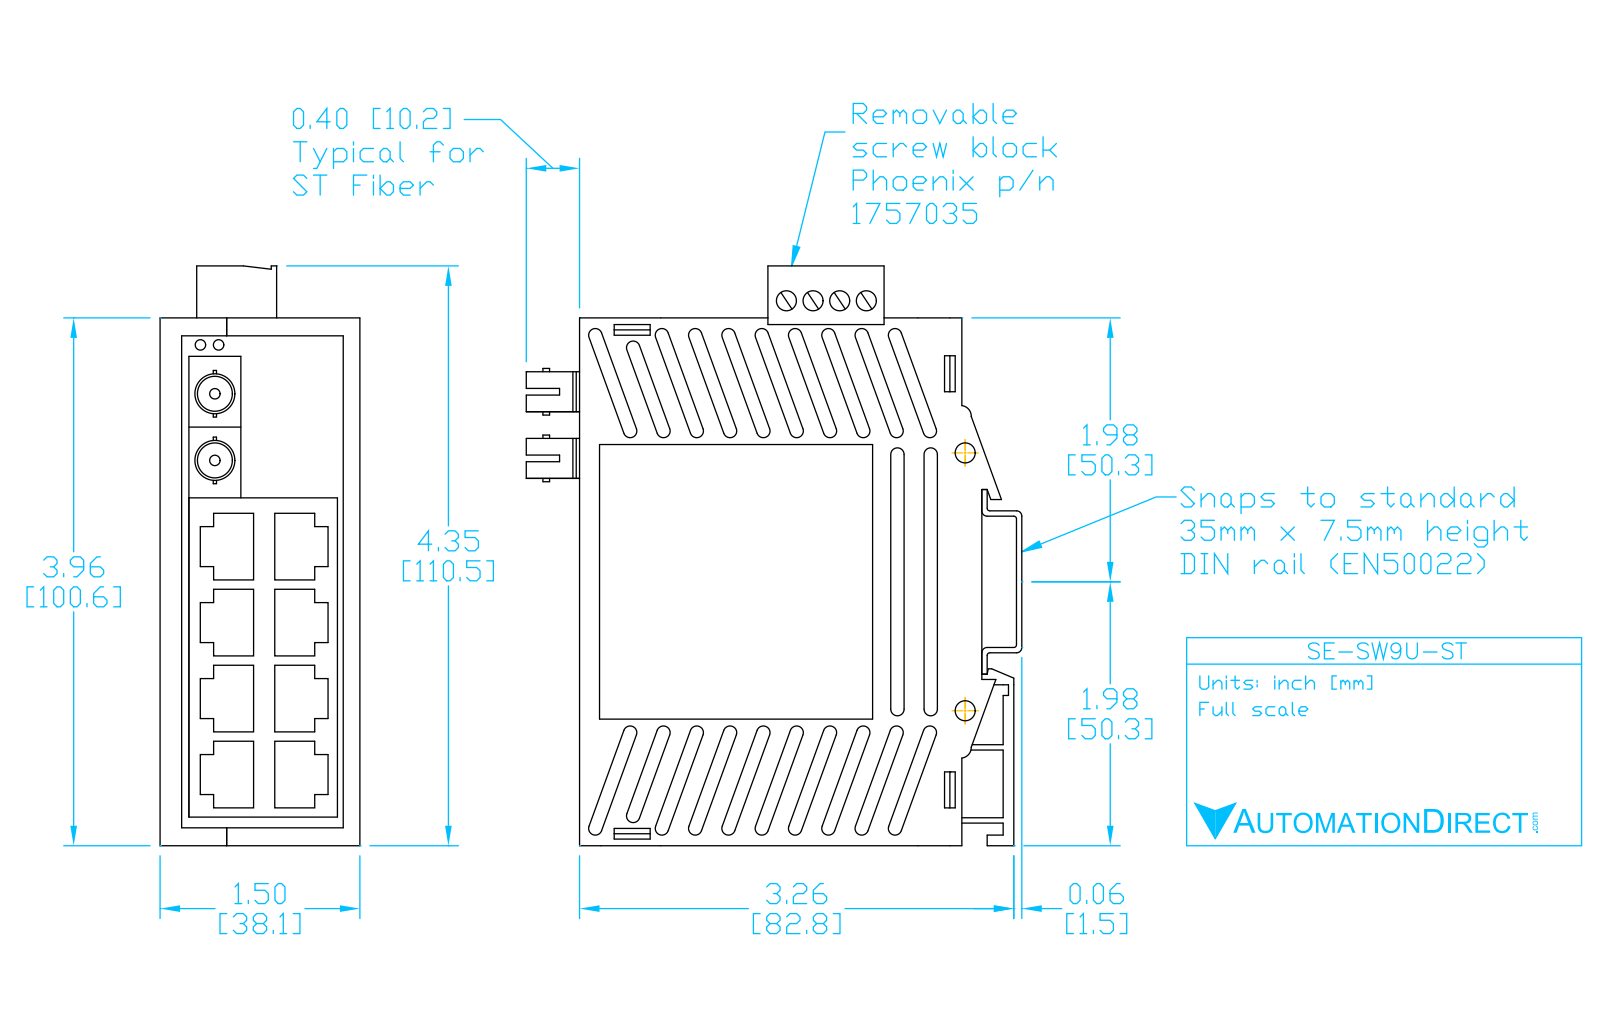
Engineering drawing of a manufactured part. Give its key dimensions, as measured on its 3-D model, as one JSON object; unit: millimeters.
{"part_name": "SE-SW9U-ST", "step_written_by": "SolidWorks 2011 (AUTOMOTIVE_DESIGN)", "units": "millimeters", "bodies": {"solids": 30, "faces": 1121, "planar": 789, "cylindrical": 269, "other": 63}, "overall_size": [109.51, 93.01, 38.75], "volume_mm3": 48040, "surface_area_mm2": 75757, "round_holes": [[3.81, 6], [6.94, 2], [2.05, 1]], "round_bosses_or_shafts": [[7.94, 2], [5.81, 1], [1.3, 1]], "partial_cylinders_radius": [[1.27, 44], [2.27, 44], [1.02, 1], [1.05, 1], [1.11, 1], [2.02, 1], [2.03, 1], [2.05, 1]], "face_to_face_distances": [1, 37.5, 1.25, 37.25, 38.5, 36.25, 38.25, 99.58, 38.75, 37.75], "hole_center_spacings": [5.08, 10.16, 7.01, 12.7, 15.24, 34.57, 37.58, 41.01]}
